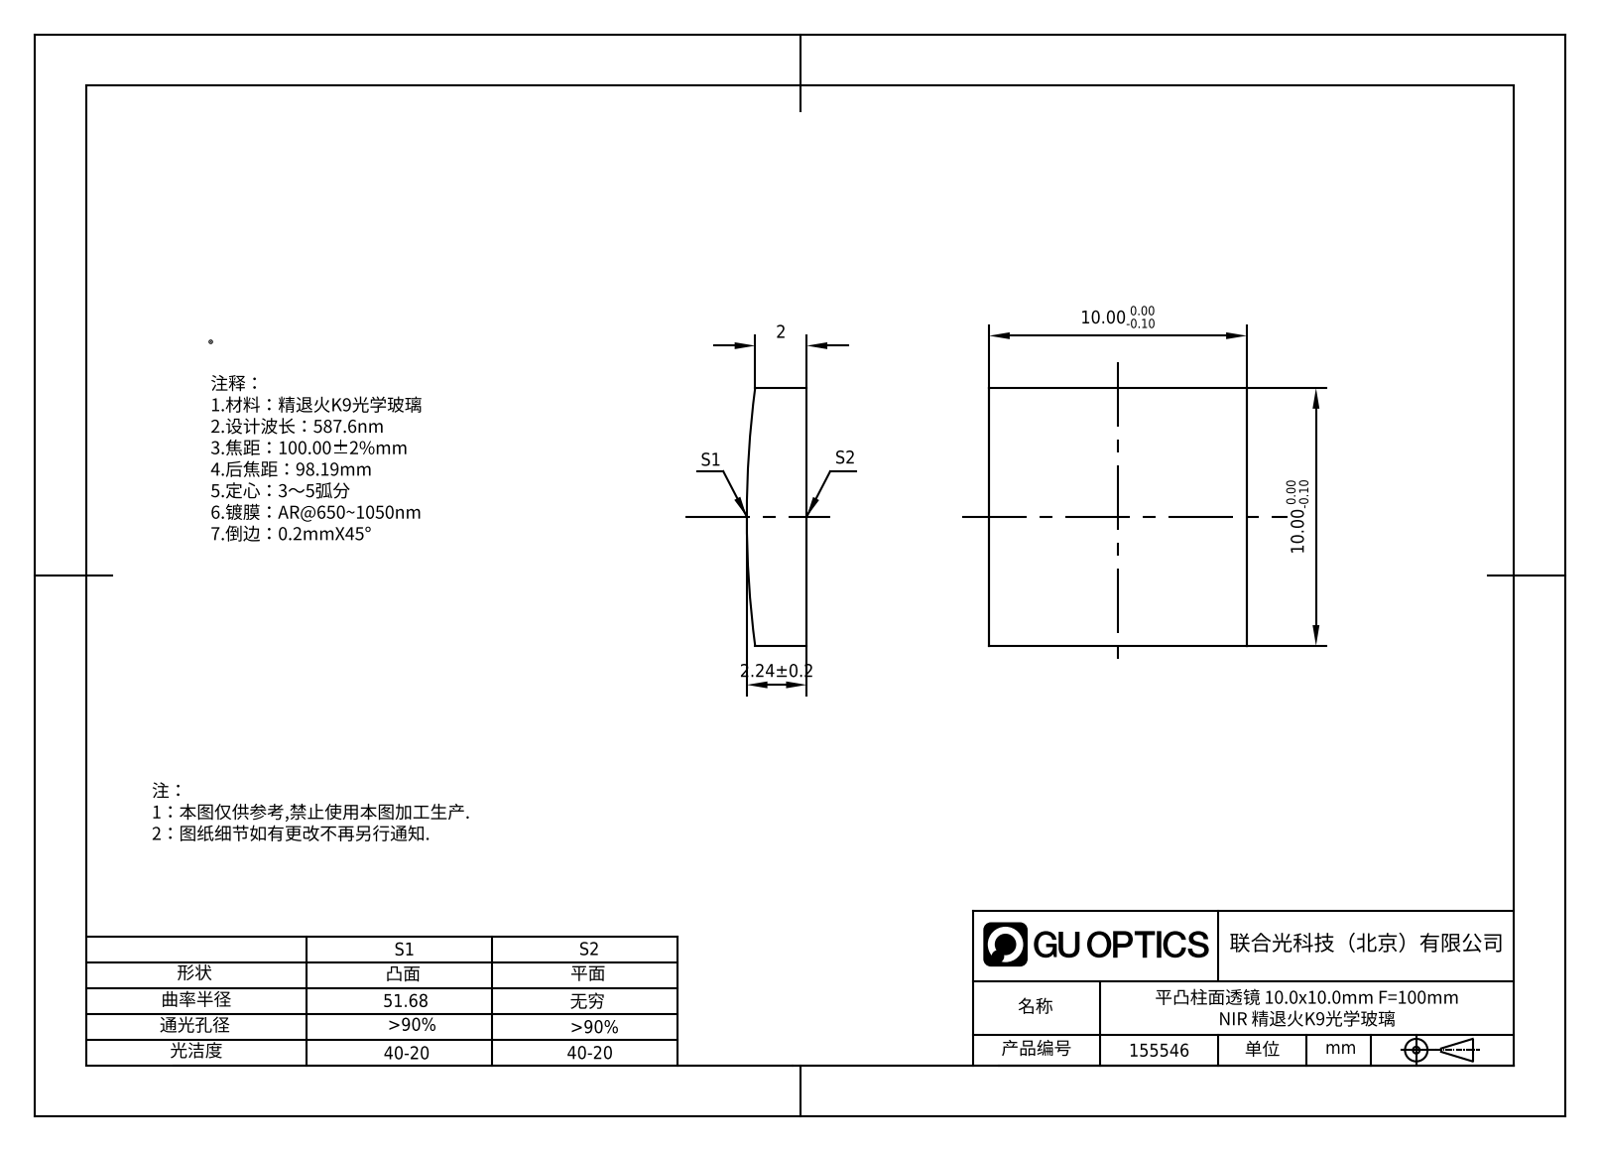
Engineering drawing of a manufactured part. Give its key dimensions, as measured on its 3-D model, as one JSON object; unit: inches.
{"part_name": "155522", "step_written_by": "SolidWorks 2020 (CONFIG_CONTROL_DESIGN)", "units": "inches", "bodies": {"solids": 1, "faces": 7, "planar": 5, "cylindrical": 2, "other": 0}, "overall_size": [0.394, 0.394, 0.088], "volume_in3": 0.013, "surface_area_in2": 0.439, "partial_cylinders_radius": [[2.035, 1]], "face_to_face_distances": [0.394]}
